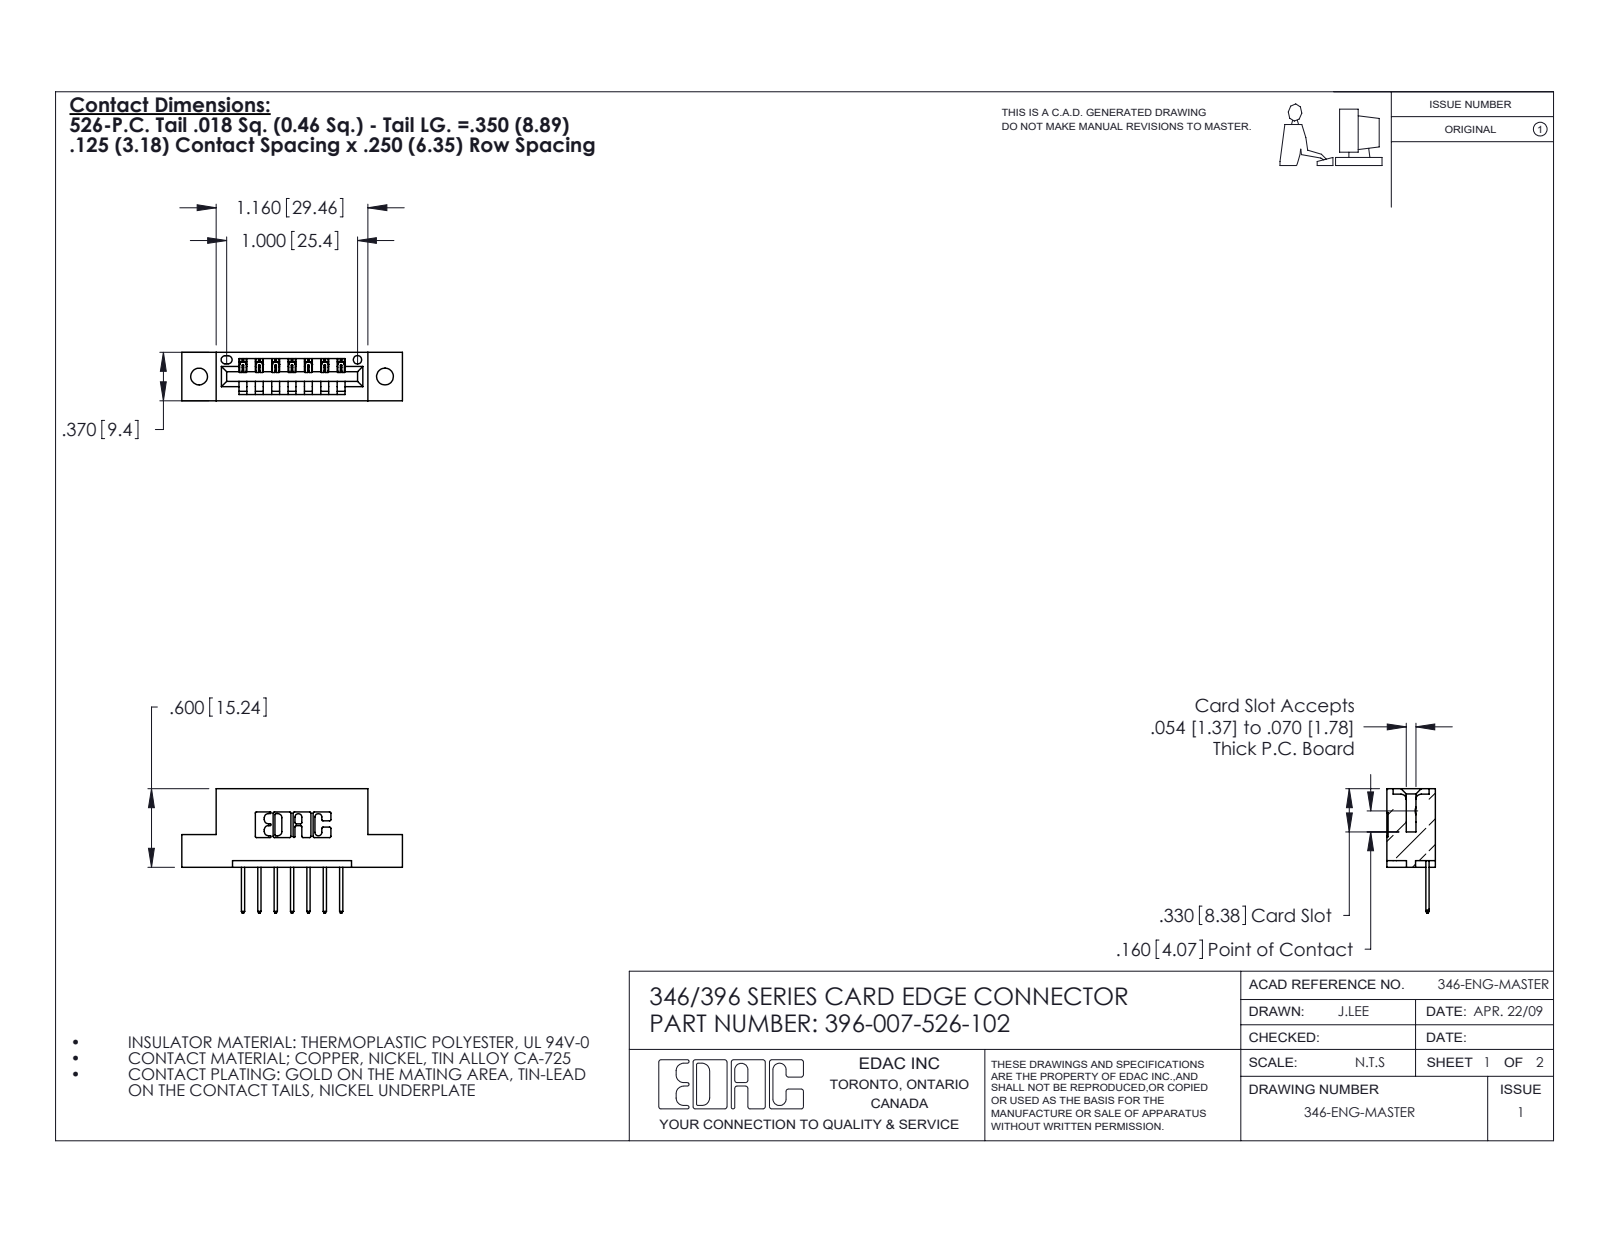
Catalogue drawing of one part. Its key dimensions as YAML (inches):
part_name: "345-292-001_345-293-126; 396-007-526-102; 346 Part_Flush Mounting Lugs - 0.128 Dia"
step_written_by: "SolidWorks 2020 (CONFIG_CONTROL_DESIGN)"
units: inches
bodies: {solids: 8, faces: 528, planar: 356, cylindrical: 172, other: 0}
overall_size: [1.685, 0.95, 0.37]
volume: 0.233
surface_area: 6.371
round_holes:
  - {diameter: 0.128, count: 2}
  - {diameter: 0.064, count: 1}
partial_cylinders:
  - {radius: 0.01, count: 22}
  - {radius: 0.006, count: 14}
  - {radius: 0.01, count: 14}
  - {radius: 0.007, count: 6}
  - {radius: 0.031, count: 6}
  - {radius: 0.026, count: 3}
  - {radius: 0.031, count: 2}
  - {radius: 0.04, count: 2}
face_to_face_distances: [0.25, 0.37, 0.048, 0.322, 0.148, 0.222, 0.1, 0.174, 0.072, 0.298]
hole_center_spacings: [0.246, 1.217, 1.42]
